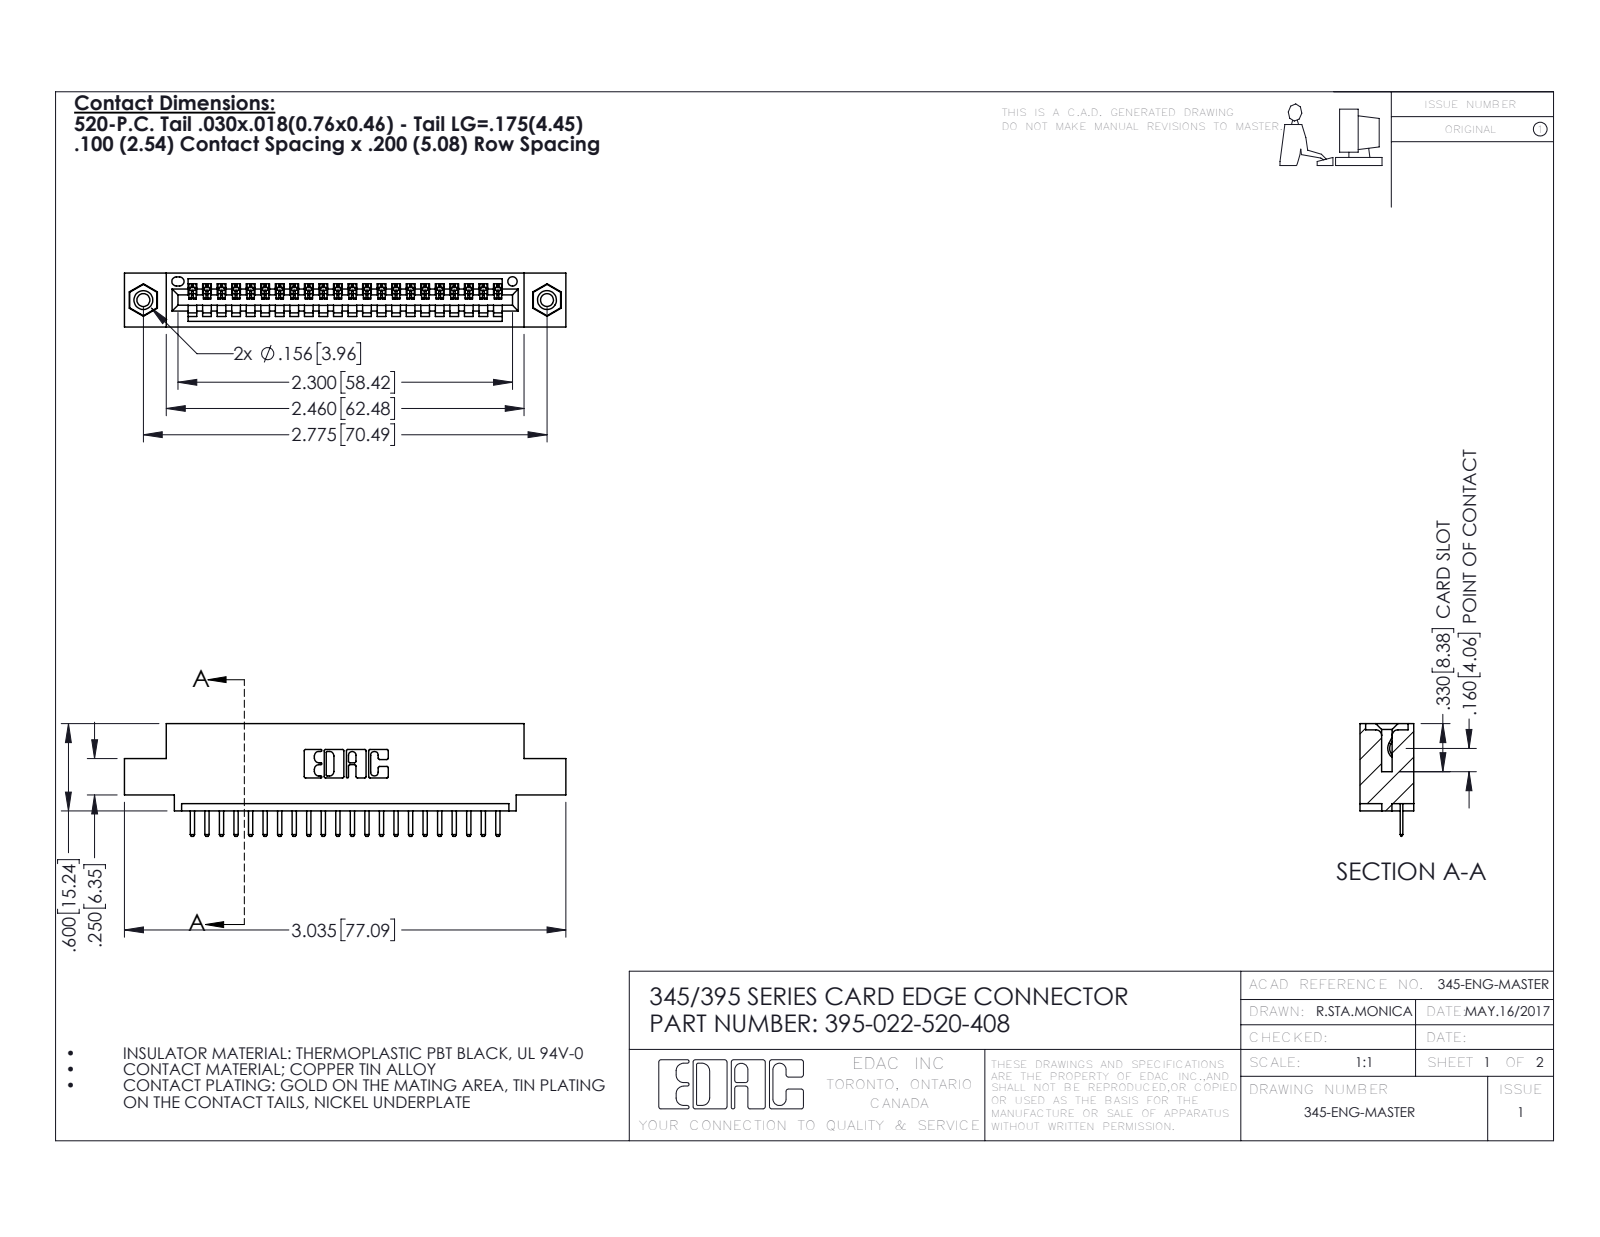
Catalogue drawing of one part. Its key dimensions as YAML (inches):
part_name: "395-022-520-408; 345-250-001_345-250-003-102; 345-292-001_345-293-120; 345 Part_0.110 Offset - 0.156 Dia-TI"
step_written_by: "SolidWorks 2016 (CONFIG_CONTROL_DESIGN)"
units: inches
bodies: {solids: 25, faces: 1554, planar: 1040, cylindrical: 498, other: 16}
overall_size: [3.035, 0.775, 0.37]
volume: 0.428
surface_area: 13.86
round_holes:
  - {diameter: 0.089, count: 2}
  - {diameter: 0.125, count: 2}
  - {diameter: 0.156, count: 2}
  - {diameter: 0.064, count: 1}
round_bosses_or_shafts:
  - {diameter: 0.155, count: 2}
partial_cylinders:
  - {radius: 0.01, count: 46}
  - {radius: 0.006, count: 44}
  - {radius: 0.01, count: 22}
  - {radius: 0.007, count: 6}
  - {radius: 0.031, count: 6}
  - {radius: 0.026, count: 3}
  - {radius: 0.031, count: 2}
  - {radius: 0.04, count: 2}
face_to_face_distances: [0.072, 0.298, 0.37, 0.2, 0.098, 0.272, 0.025, 0.225, 0.072, 0.149]
hole_center_spacings: [0.27, 2.541, 2.775]
